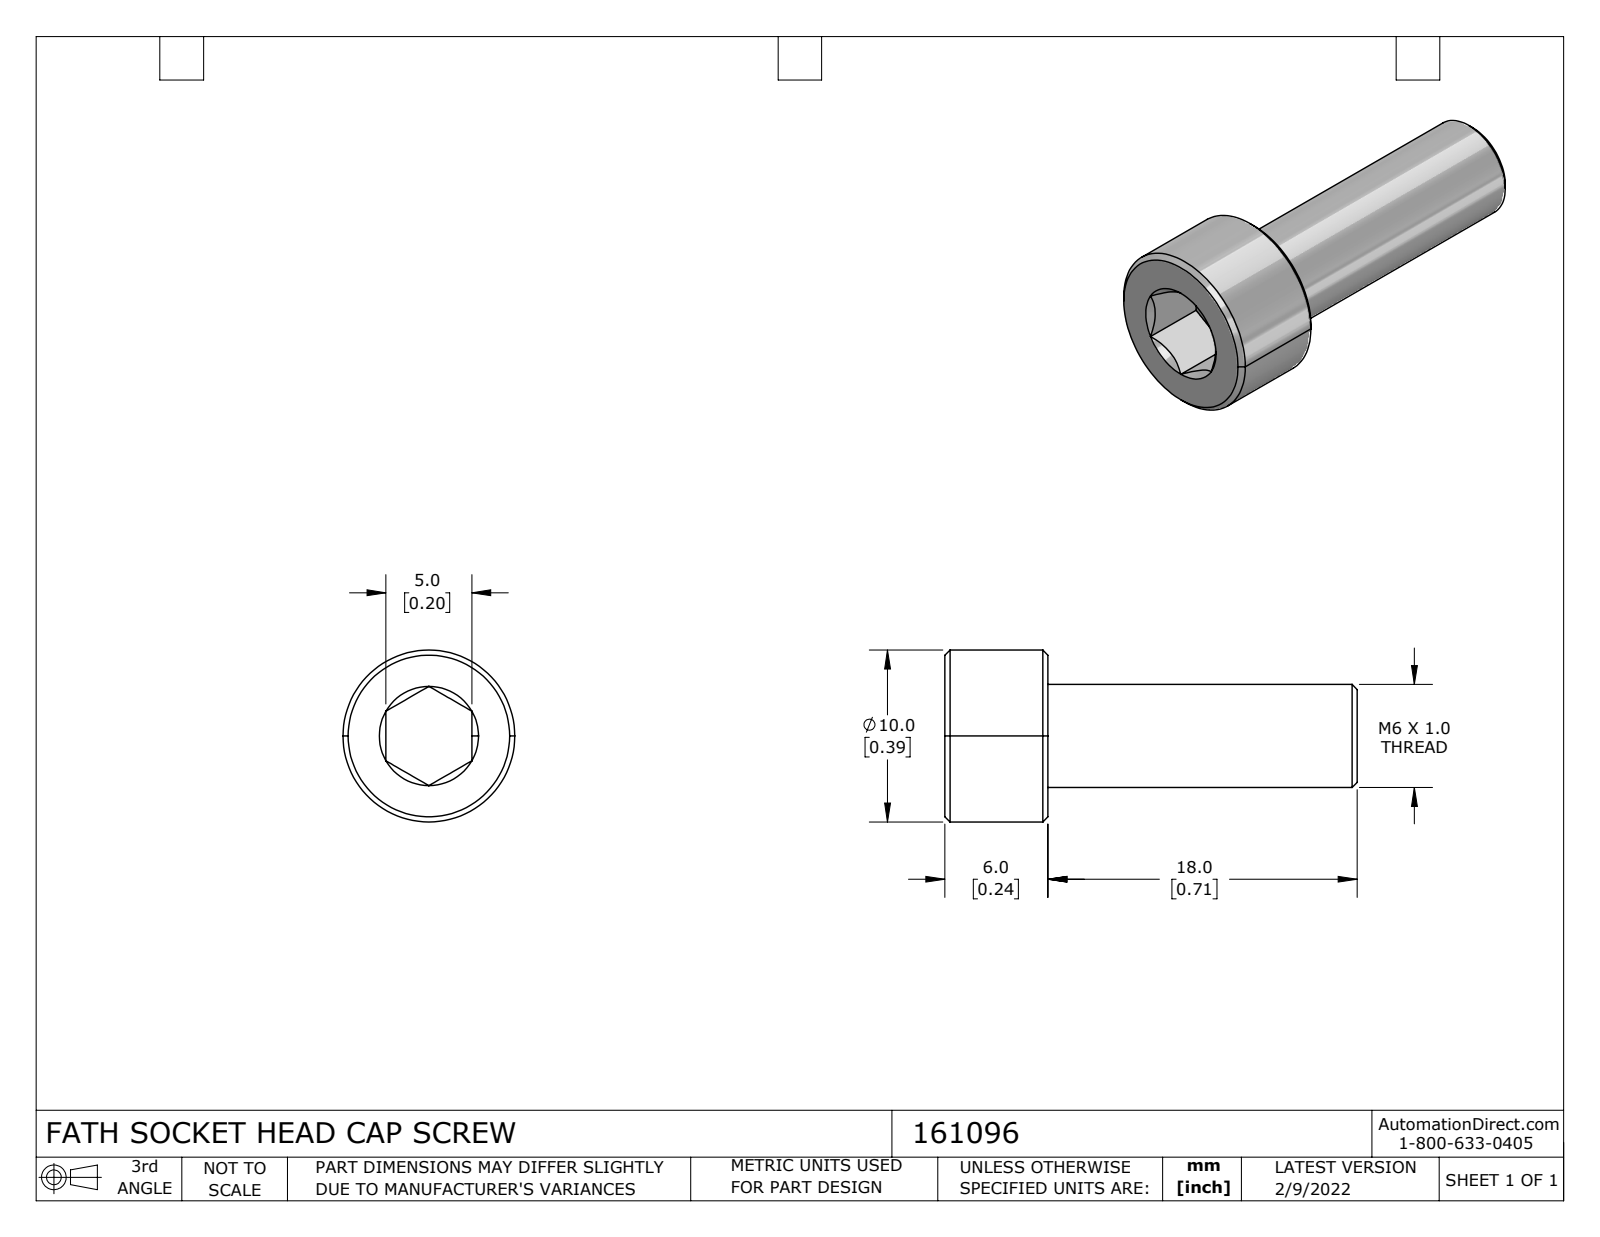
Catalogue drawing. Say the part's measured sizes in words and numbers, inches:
The part is named "161096". Its 3-D file was written by "SolidWorks 2021 (CONFIG_CONTROL_DESIGN)". It is 1 solid with 27 faces: 10 planar, 4 cylindrical and 13 other. Overall it measures 0.945 by 0.394 by 0.394 inches. Its volume is 0.055 cubic inches and its surface area 1.14 square inches. Round bosses or shafts: 1 of diameter 0.394, 1 of diameter 0.236. The main face-to-face distances are 0.236, 0.197, 0.945, 0.709, 0.148, 0.089, 0.797.
